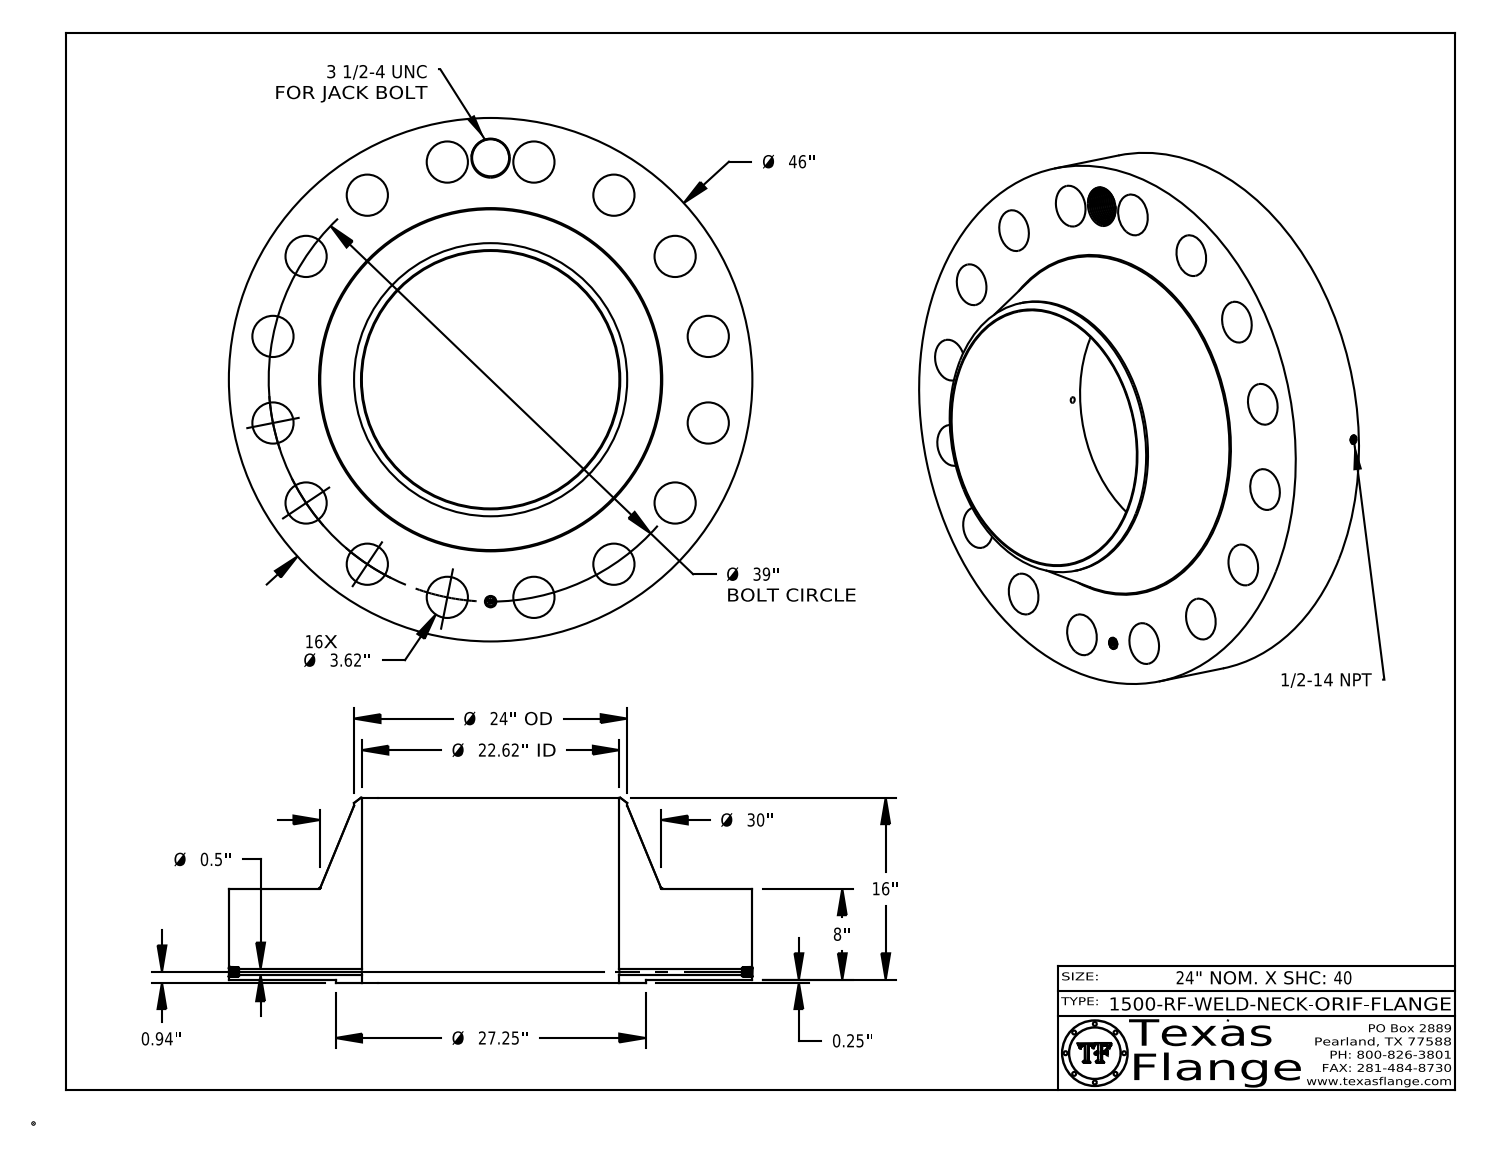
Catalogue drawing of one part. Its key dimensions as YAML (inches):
part_name: "1500-RF-WELD-NECK"
step_written_by: "CATIA V5 STEP AP214 (AUTOMOTIVE_DESIGN)"
units: inches
bodies: {solids: 1, faces: 887, planar: 369, cylindrical: 144, other: 374}
overall_size: [46, 46, 16.25]
volume: 10017
surface_area: 6563
round_holes:
  - {diameter: 3.62, count: 16}
  - {diameter: 0.5, count: 1}
  - {diameter: 0.672, count: 1}
  - {diameter: 1, count: 1}
  - {diameter: 3.25, count: 1}
  - {diameter: 22.624, count: 1}
round_bosses_or_shafts:
  - {diameter: 0.061, count: 8}
  - {diameter: 46, count: 1}
  - {diameter: 27.25, count: 1}
  - {diameter: 24, count: 1}
  - {diameter: 0.788, count: 1}
face_to_face_distances: [8, 0.25, 8.25, 16.25, 16, 8.235, 7.985, 0.015, 8.015, 0.298]
hole_center_spacings: [19.5, 27.577, 36.031, 32.427, 7.608, 14.924, 14.925, 21.667]
